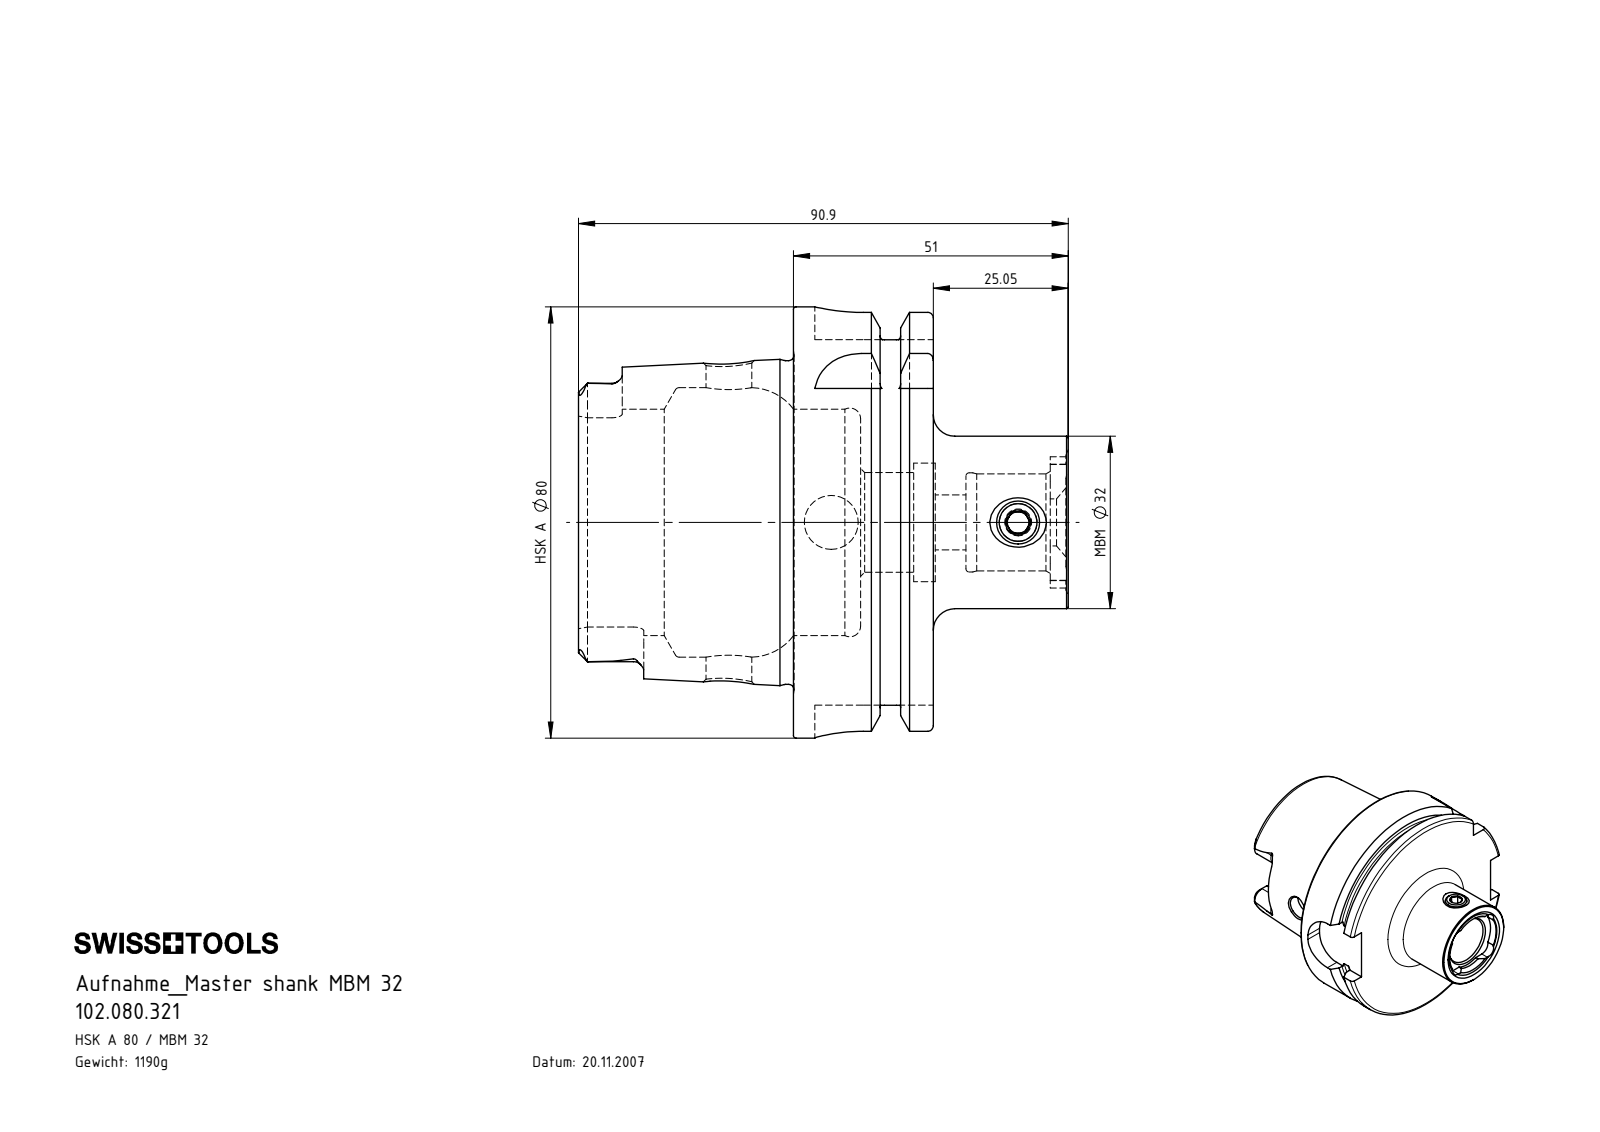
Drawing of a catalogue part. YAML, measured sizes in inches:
part_name: "HA8-MB3.K01.051_B_Fertigbearbeitung; MB3-ER1.001.011_A; 102.080.321"
step_written_by: "SolidWorks 2017 (CONFIG_CONTROL_DESIGN)"
units: inches
bodies: {solids: 2, faces: 223, planar: 70, cylindrical: 66, other: 87}
overall_size: [3.579, 3.15, 3.15]
volume: 9.247
surface_area: 57.67
round_holes:
  - {diameter: 0.157, count: 1}
  - {diameter: 0.276, count: 1}
  - {diameter: 0.335, count: 1}
  - {diameter: 0.394, count: 1}
  - {diameter: 0.402, count: 1}
  - {diameter: 0.709, count: 1}
  - {diameter: 0.724, count: 1}
  - {diameter: 0.728, count: 1}
  - {diameter: 0.866, count: 1}
  - {diameter: 1.654, count: 1}
  - {diameter: 1.969, count: 1}
round_bosses_or_shafts:
  - {diameter: 3.15, count: 1}
  - {diameter: 2.754, count: 1}
  - {diameter: 2.365, count: 1}
  - {diameter: 1.26, count: 1}
  - {diameter: 0.315, count: 1}
partial_cylinders:
  - {radius: 0.075, count: 6}
  - {radius: 0.126, count: 4}
  - {radius: 0.153, count: 4}
  - {radius: 0.354, count: 4}
  - {radius: 0.413, count: 1}
  - {radius: 0.48, count: 1}
face_to_face_distances: [1.022, 0.49, 0.531, 1.571, 2.061, 2.593, 2.669, 2.606, 1.035, 0.545]
hole_center_spacings: [1.366]
